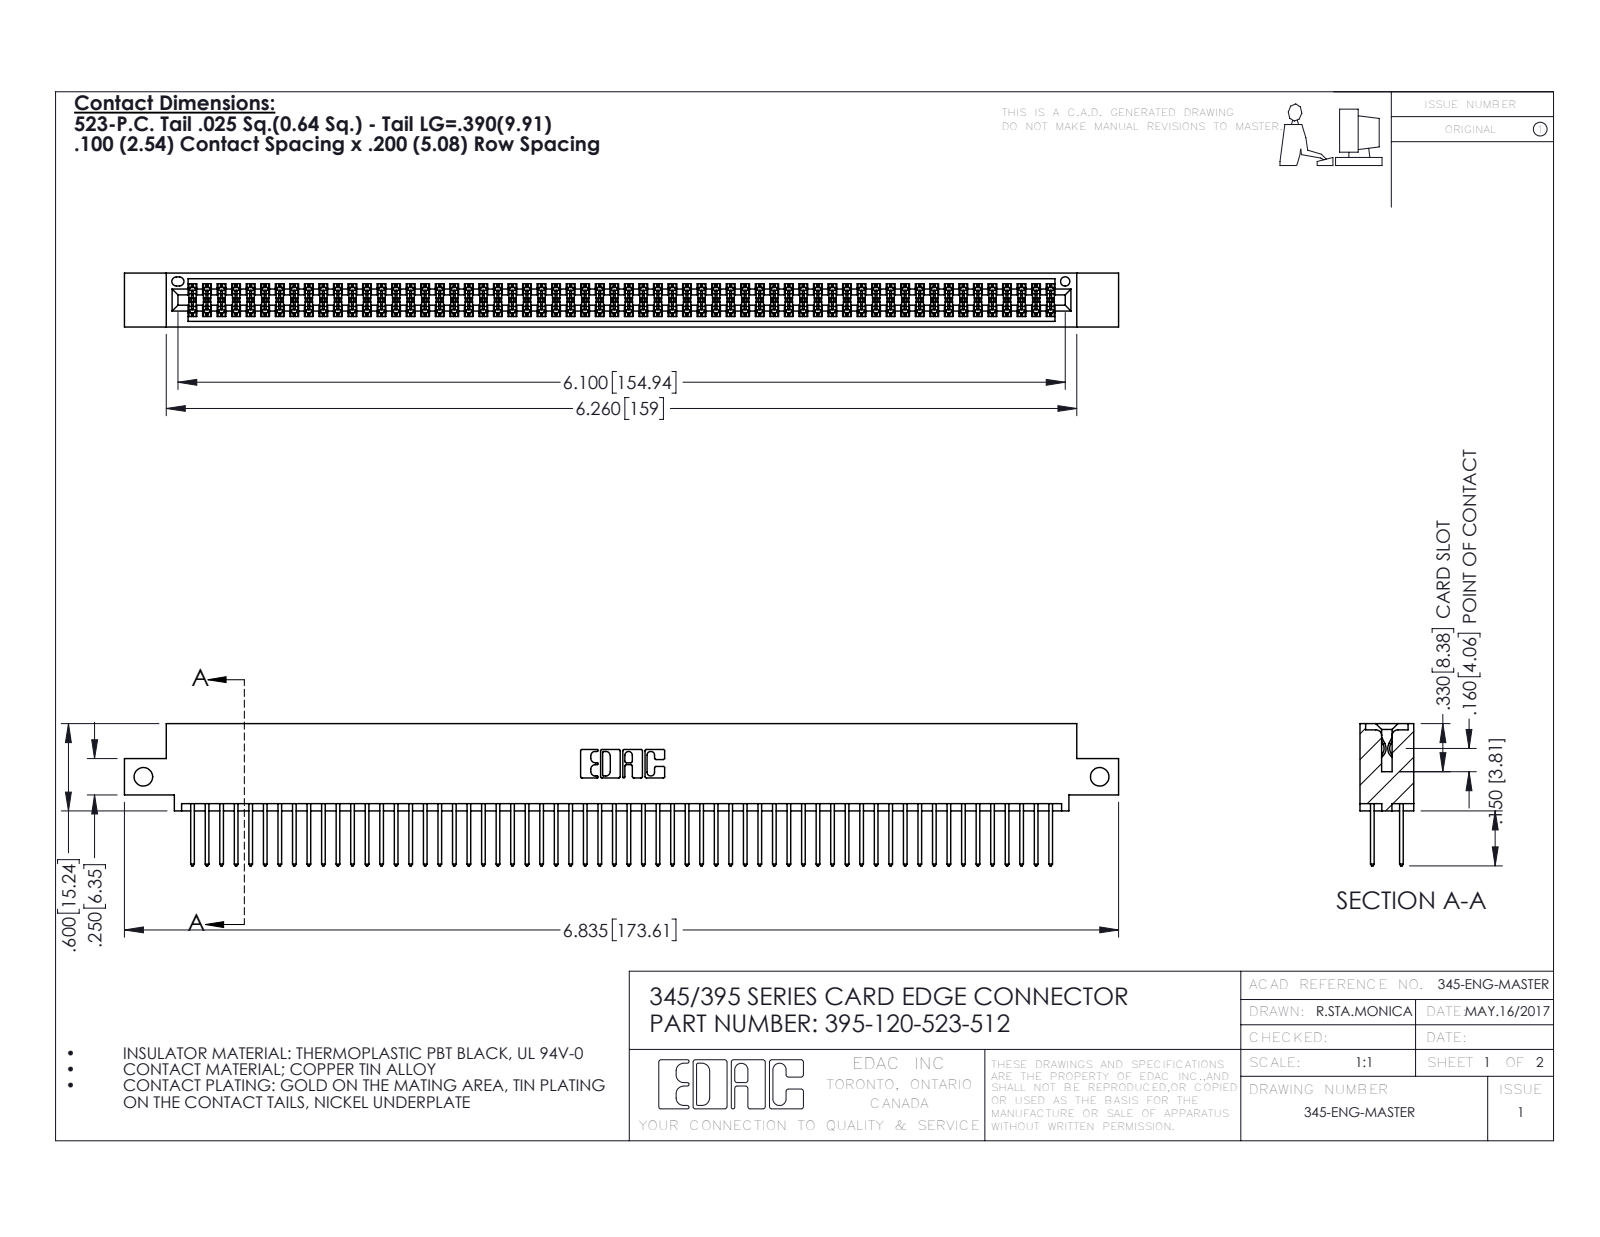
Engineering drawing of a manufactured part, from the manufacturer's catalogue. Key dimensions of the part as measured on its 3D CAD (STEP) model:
Part name (STEP PRODUCT): 395-120-523-512; 345-292-001_345-293-123; 345 Part_0.110 Offset - Side Mount
STEP written by: SolidWorks 2016 (CONFIG_CONTROL_DESIGN)
Units: inches
Bodies: 121 solids, 6130 faces (4044 planar, 2086 cylindrical, 0 other)
Overall size (bounding box): 6.835 × 0.977 × 0.37
Volume: 1.045 in³ · Surface area: 41.4 in²
Round holes (diameter × count): ⌀0.128 ×2, ⌀0.064 ×1
Partial cylindrical surfaces — rounded edges, fillets, slot ends (radius × count): R0.006 ×180, R0.01 ×120, R0.01 ×22, R0.007 ×6, R0.031 ×6, R0.026 ×3, R0.014 ×2, R0.019 ×2
Main face-to-face distances: 0.298, 0.072, 0.2, 0.098, 0.272, 0.025, 0.37, 0.225, 0.175, 0.149
Hole centre spacings: 6.575
